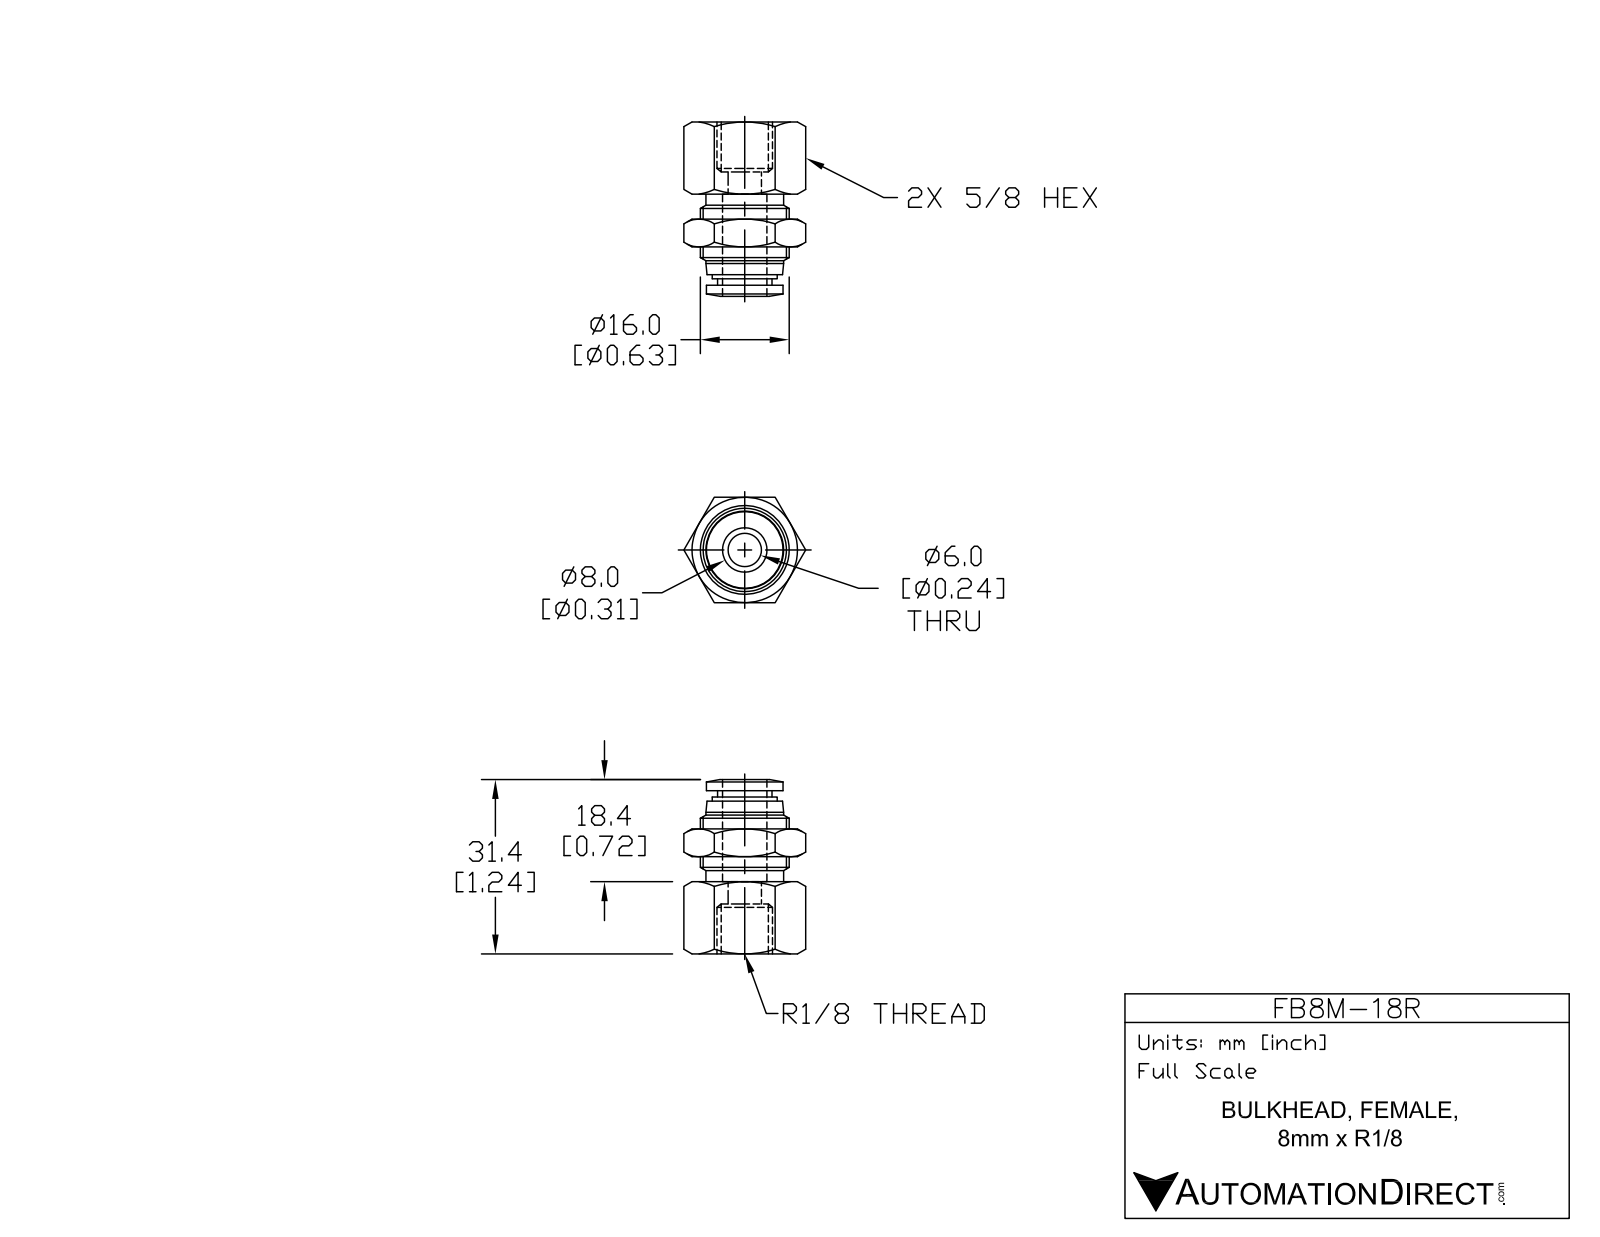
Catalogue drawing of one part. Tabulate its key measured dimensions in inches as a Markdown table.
| quantity | value |
| --- | --- |
| part name | FB8M-18R |
| STEP written by | SolidWorks 2015 (AUTOMOTIVE_DESIGN) |
| units | inches |
| bodies | 1 solid, 80 faces (22 planar, 18 cylindrical, 40 other) |
| overall size | 1.236 × 0.864 × 0.748 |
| volume | 0.364 in³ |
| surface area | 5.427 in² |
| round holes (diameter × count) | 0.236 × 1, 0.327 × 1 |
| round bosses / shafts (diameter × count) | 0.63 × 1, 0.551 × 1, 0.543 × 1, 0.461 × 1, 0.386 × 1 |
| main face-to-face distances | 0.748, 0.512, 0.677, 0.165, 0.874, 0.362, 0.197, 1.157, 0.646, 0.481 |
